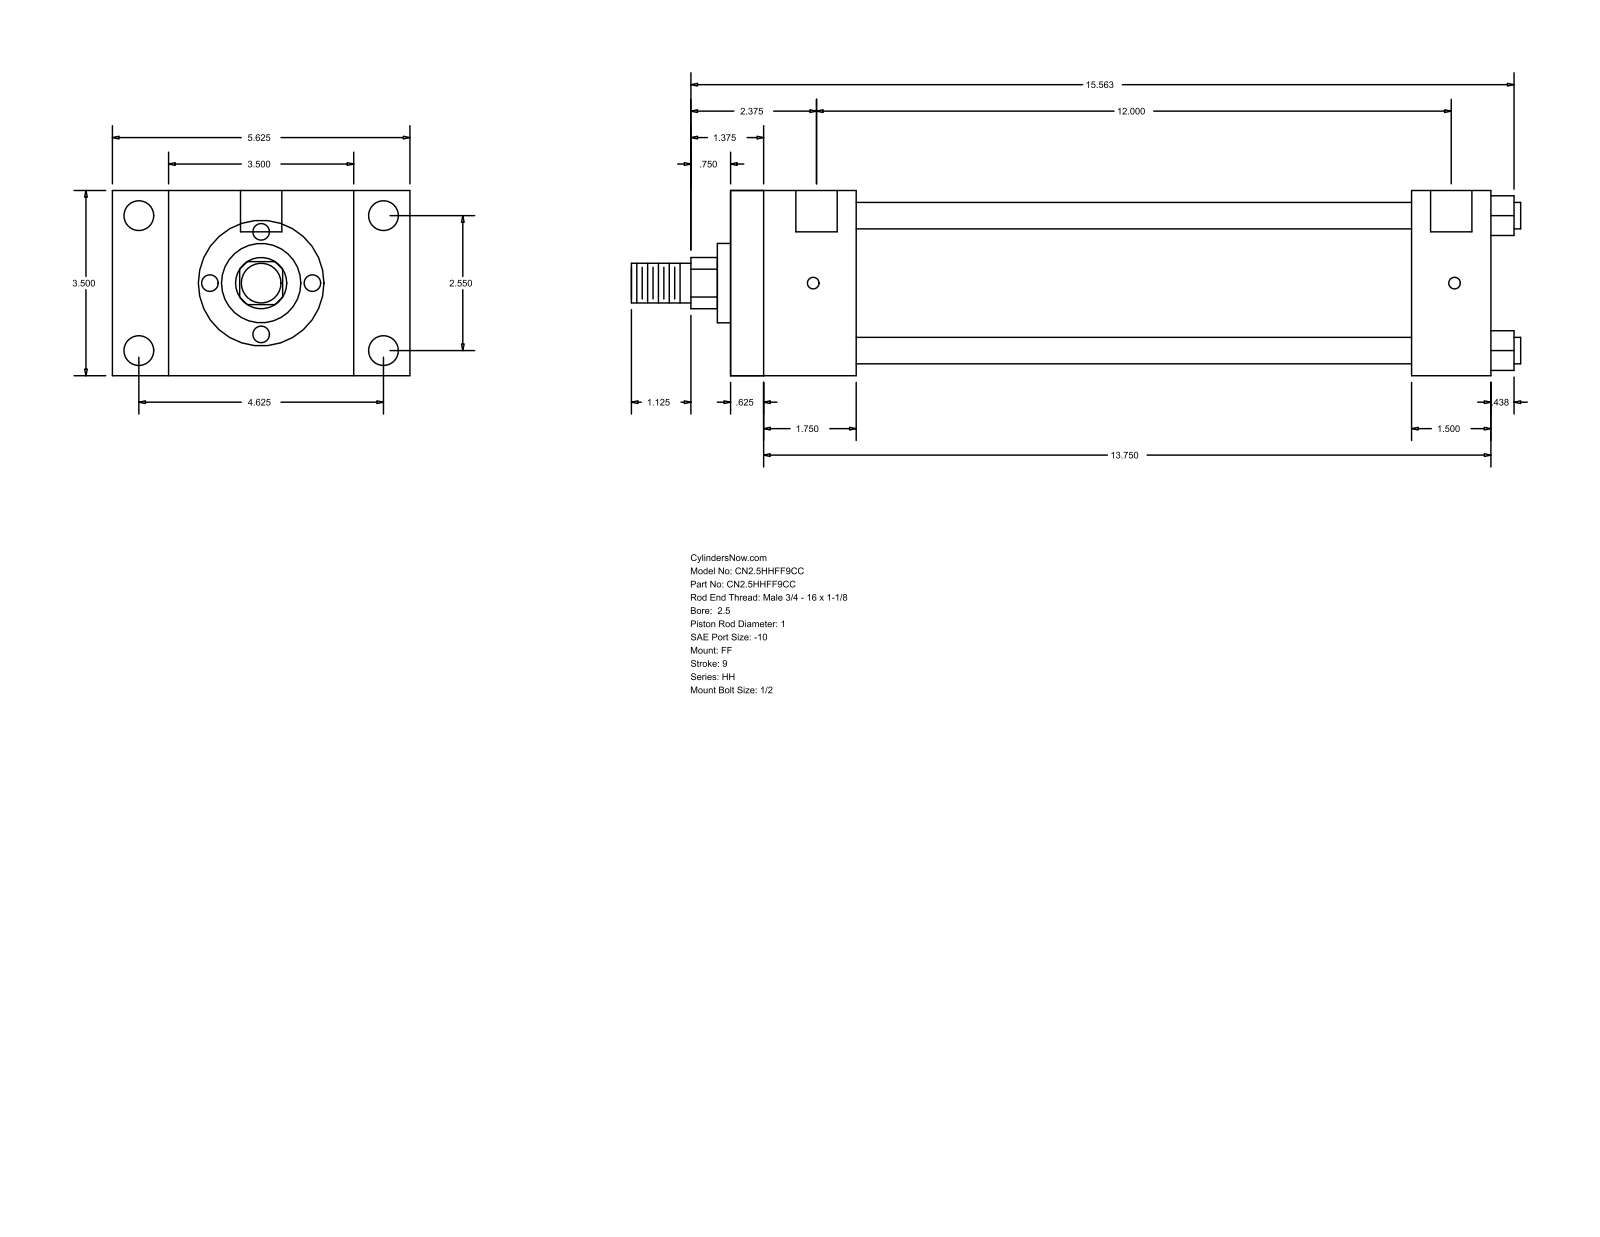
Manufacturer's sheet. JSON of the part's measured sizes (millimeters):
{"part_name": "HH_FF__0250_1", "step_written_by": "GSSL Pune (CONFIG_CONTROL_DESIGN)", "units": "millimeters", "bodies": {"solids": 0, "faces": 92, "planar": 64, "cylindrical": 28, "other": 0}, "overall_size": [427.04, 142.88, 88.9], "round_holes": [[5.56, 4], [14.3, 4], [19.84, 2]], "round_bosses_or_shafts": [[12.7, 4], [73.03, 1], [38.1, 1], [25.4, 1], [19.05, 1]], "partial_cylinders_radius": [[12.29, 1]], "face_to_face_distances": [88.9, 365.13, 15.87, 349.26, 60.33, 44.46, 304.8, 327.02, 311.15, 266.69], "hole_center_spacings": [1.59, 64.76, 117.48, 134.15, 306.38, 307.97, 304.79]}
